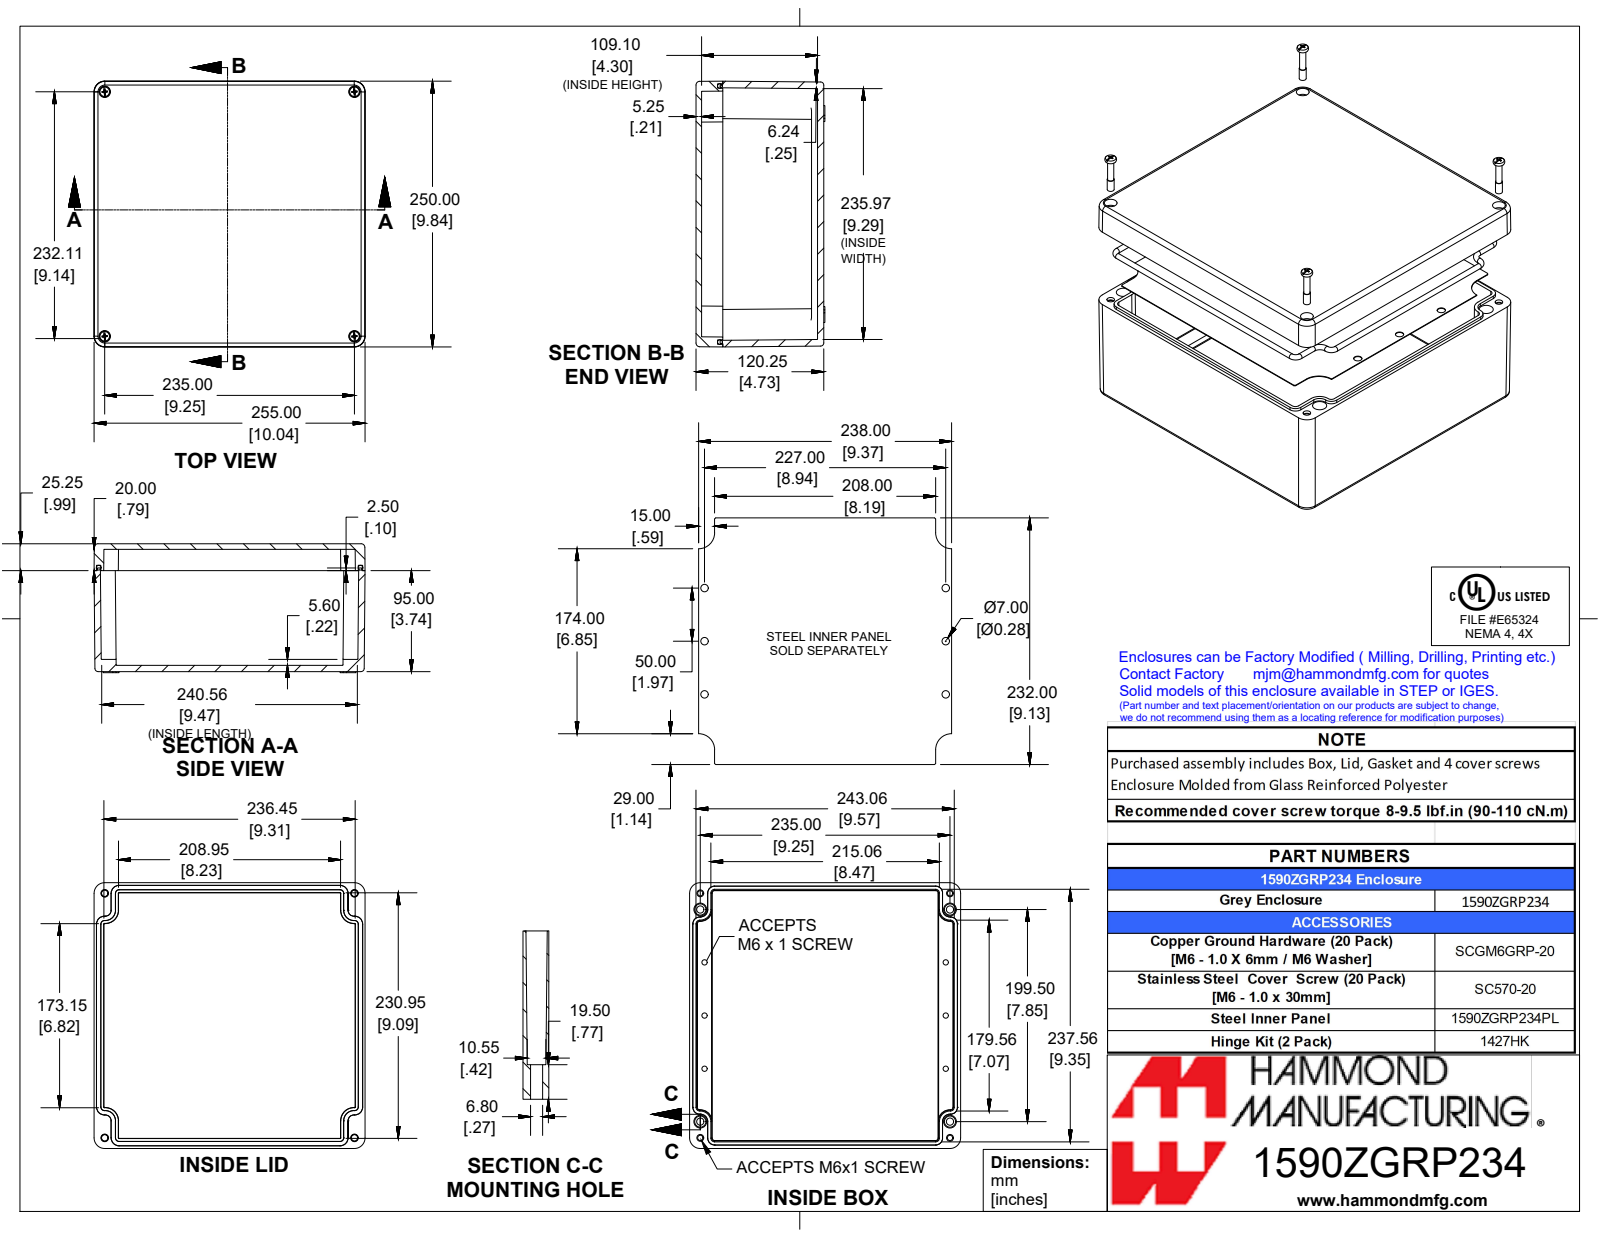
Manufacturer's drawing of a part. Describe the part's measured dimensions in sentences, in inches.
The part is named "1590ZGRP234". Its 3-D file was written by "SolidWorks 2019 (CONFIG_CONTROL_DESIGN)". It is 8 solids with 455 faces: 253 planar, 74 cylindrical and 128 other. Overall it measures 10.039 by 9.843 by 4.774 inches. Its volume is 97.29 cubic inches and its surface area 966.7 square inches. Round holes: 10 of diameter 0.194, 6 of diameter 0.276, 4 of diameter 0.236, 4 of diameter 0.252, 4 of diameter 0.268, 4 of diameter 0.425. Round bosses or shafts: 6 of diameter 0.177, 4 of diameter 0.231, 4 of diameter 0.208. Partial cylindrical surfaces (rounded edges, fillets, slot ends): 8 of radius 0.394, 6 of radius 0.02, 4 of radius 0.118, 4 of radius 0.138, 4 of radius 0.591. The main face-to-face distances are 4.734, 0.453, 4.281, 0.472, 0.02, 4.262, 4.528, 4.075, 4.055, 0.207. The hole center spacings are 9.252, 0.016, 0.585, 0.6, 1.965, 1.969, 2.548, 2.564.
